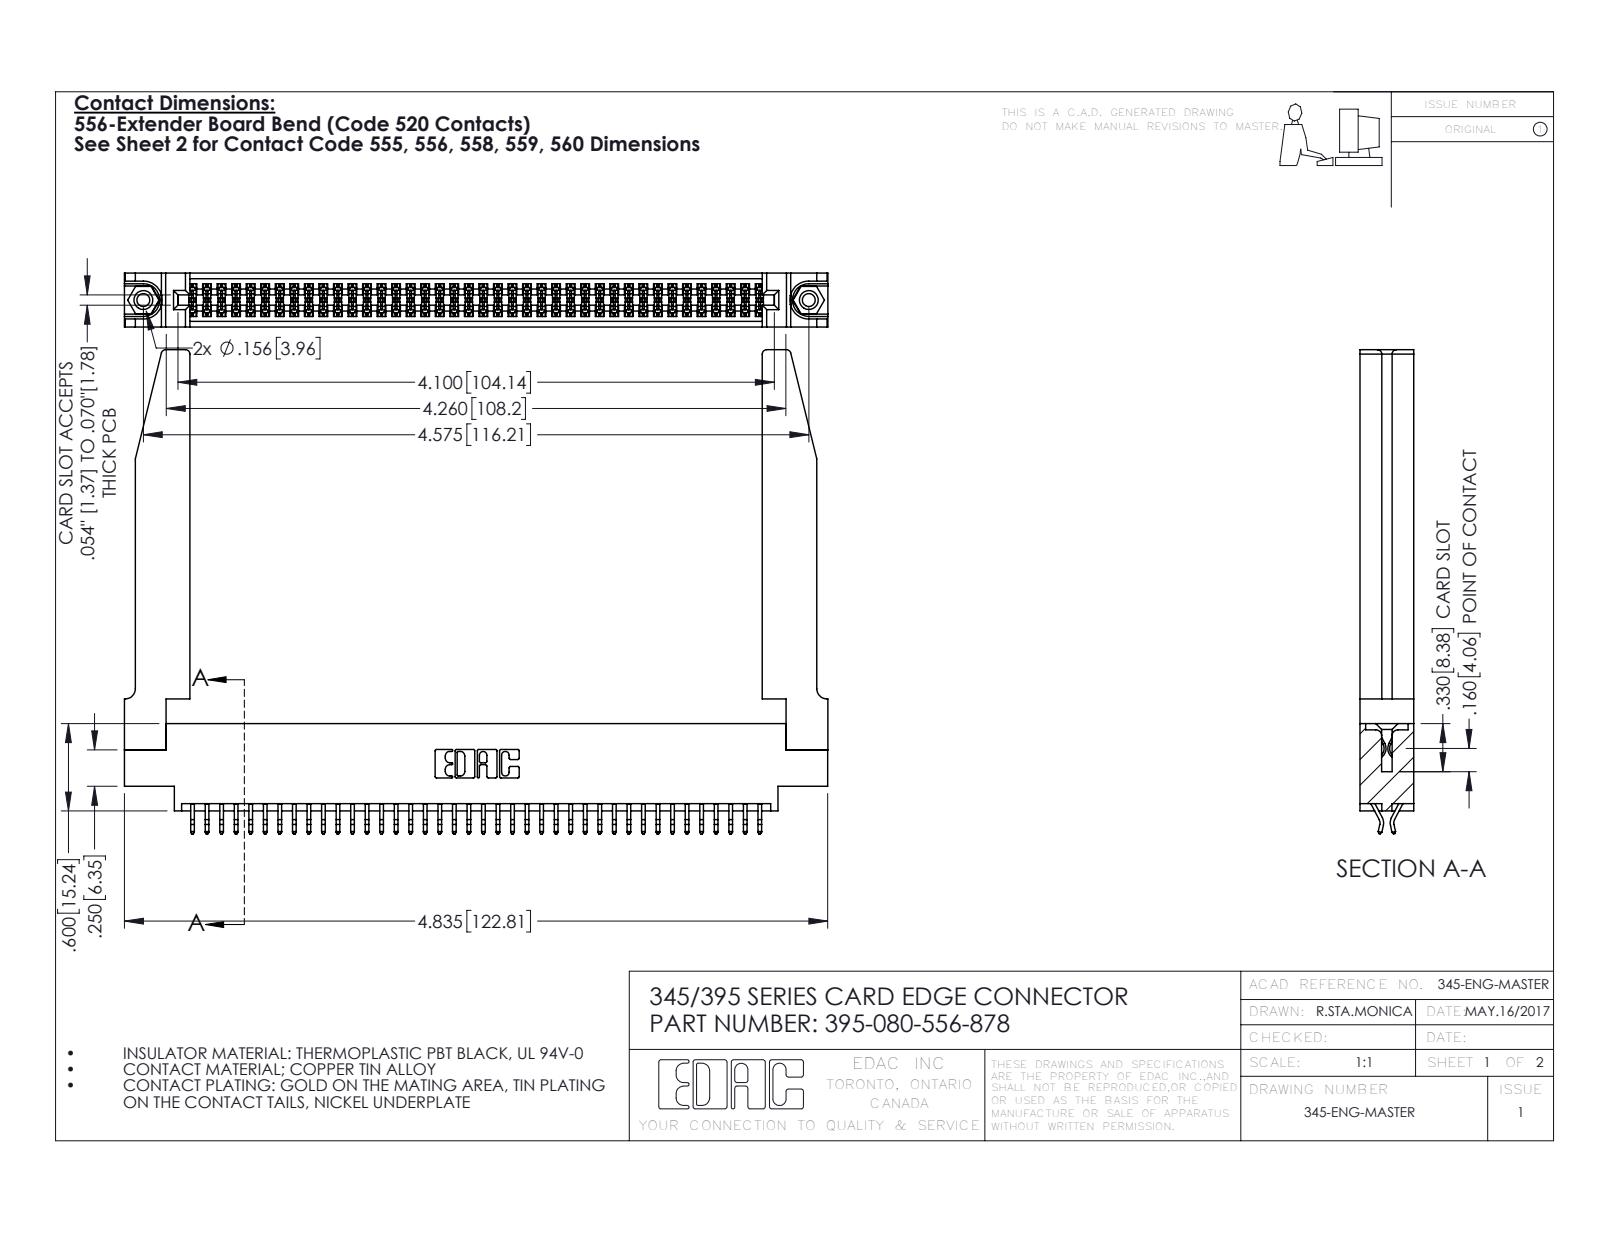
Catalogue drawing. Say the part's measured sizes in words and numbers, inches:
The part is named "345 Part_0.170 Offset - 0.156 Dia-TH; 345-250-001_345-250-001-102; 345-292-001_556 Tail; 345-220-078_345-220-078 (+1 more)". Its 3-D file was written by "SolidWorks 2016 (CONFIG_CONTROL_DESIGN)". It is 85 solids with 4844 faces: 3186 planar, 1606 cylindrical and 52 other. Overall it measures 4.836 by 3.327 by 0.37 inches. Its volume is 1.194 cubic inches and its surface area 37.68 square inches. Round holes: 2 of diameter 0.089, 2 of diameter 0.125, 2 of diameter 0.156, 1 of diameter 0.064. Round bosses or shafts: 2 of diameter 0.155. Partial cylindrical surfaces (rounded edges, fillets, slot ends): 120 of radius 0.006, 22 of radius 0.01, 8 of radius 0.03, 6 of radius 0.007, 6 of radius 0.031, 3 of radius 0.026, 2 of radius 0.01, 2 of radius 0.014. The main face-to-face distances are 0.37, 0.072, 0.298, 0.025, 0.098, 0.272, 0.2, 0.225, 0.175, 0.148. The hole center spacings are 0.27, 4.339, 4.575.
